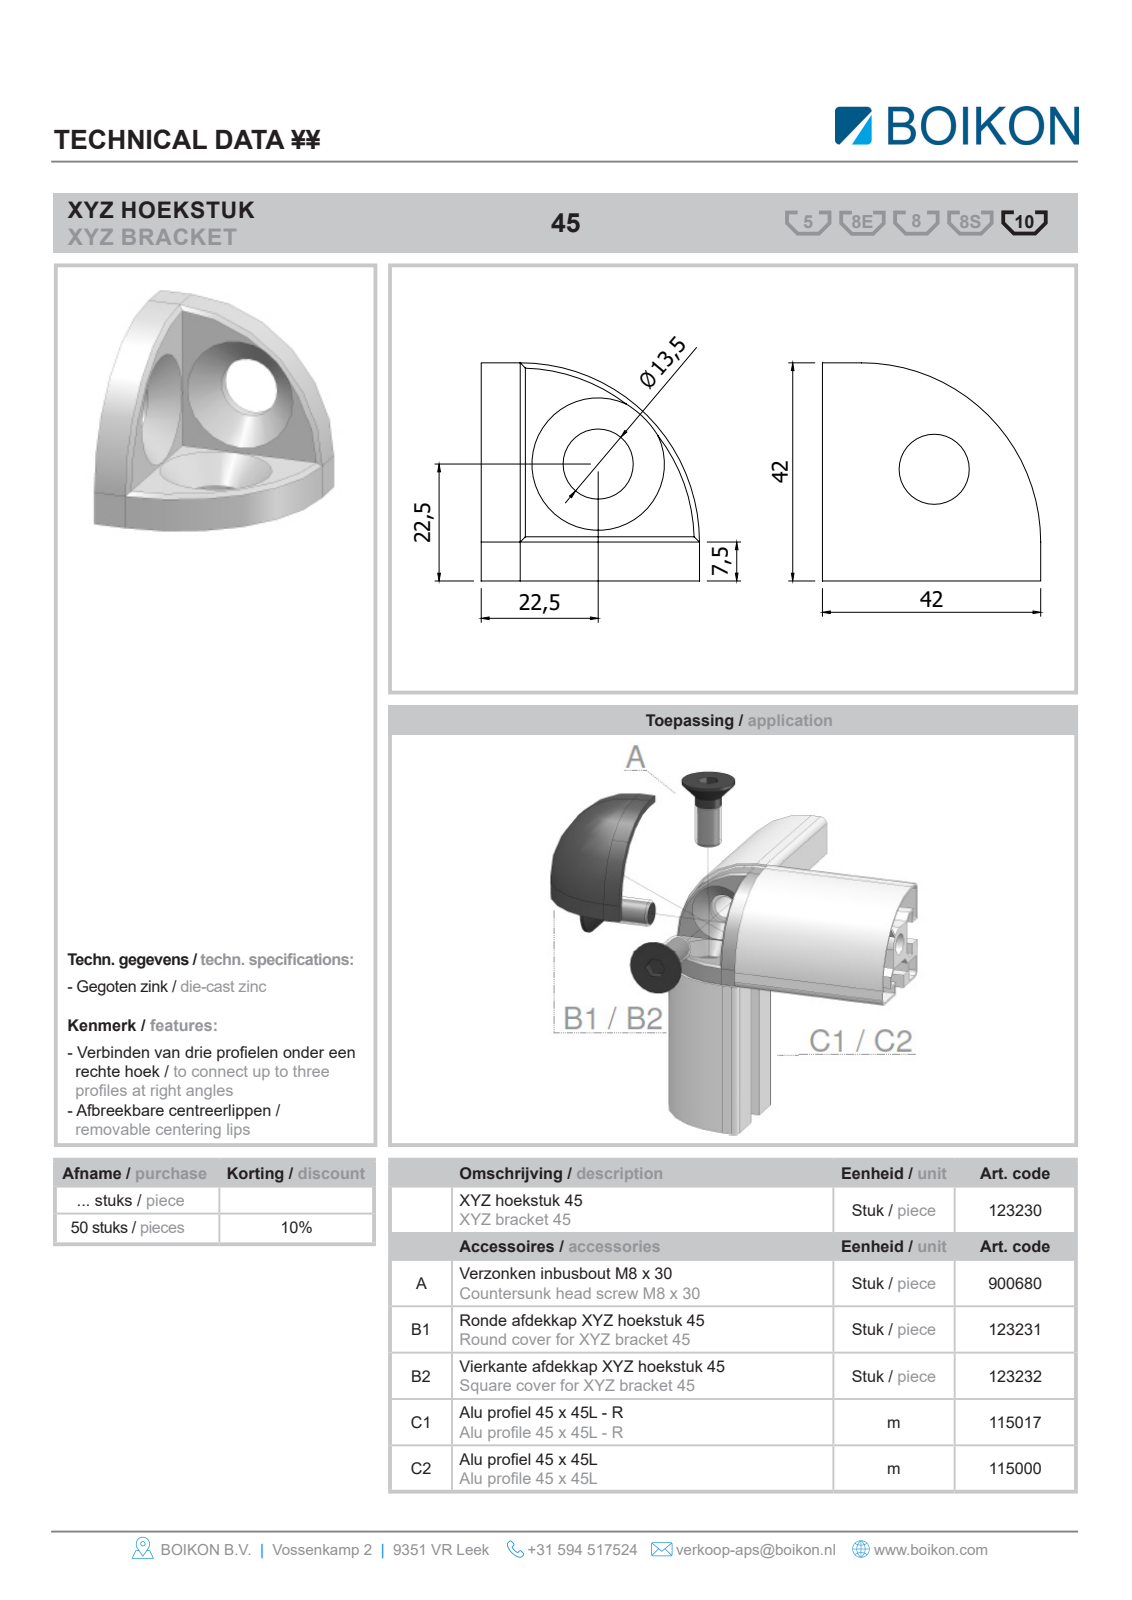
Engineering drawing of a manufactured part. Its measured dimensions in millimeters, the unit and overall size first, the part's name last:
Units: millimetres
Overall size (bounding box): 63.5 × 63.5 × 63.5
Round holes (diameter × count): ⌀13.5 ×3
Round bosses / shafts (diameter × count): ⌀24 ×3, ⌀12 ×3, ⌀9.85 ×2, ⌀9.85 ×1
Partial cylindrical surfaces — rounded edges, fillets, slot ends (radius × count): R34.5 ×3
Main face-to-face distances: 8.5, 21.5, 30, 8, 63.5, 42, 33.5, 25.7, 4.2, 4.3
Volume: 34 936 mm³ · Surface area: 14 432 mm²
Bodies: 4 solids, 63 faces (36 planar, 15 cylindrical, 12 other)
Part name (STEP PRODUCT): Root; 123230XYZ HOEKSTUK 45BOIKON; 900680Verz. inbusbout DIN 7991 EV M12 x 30BOIKON0
STEP written by: HiCAD 2013 1802.4 Build 509 (AUTOMOTIVE_DESIGN)
